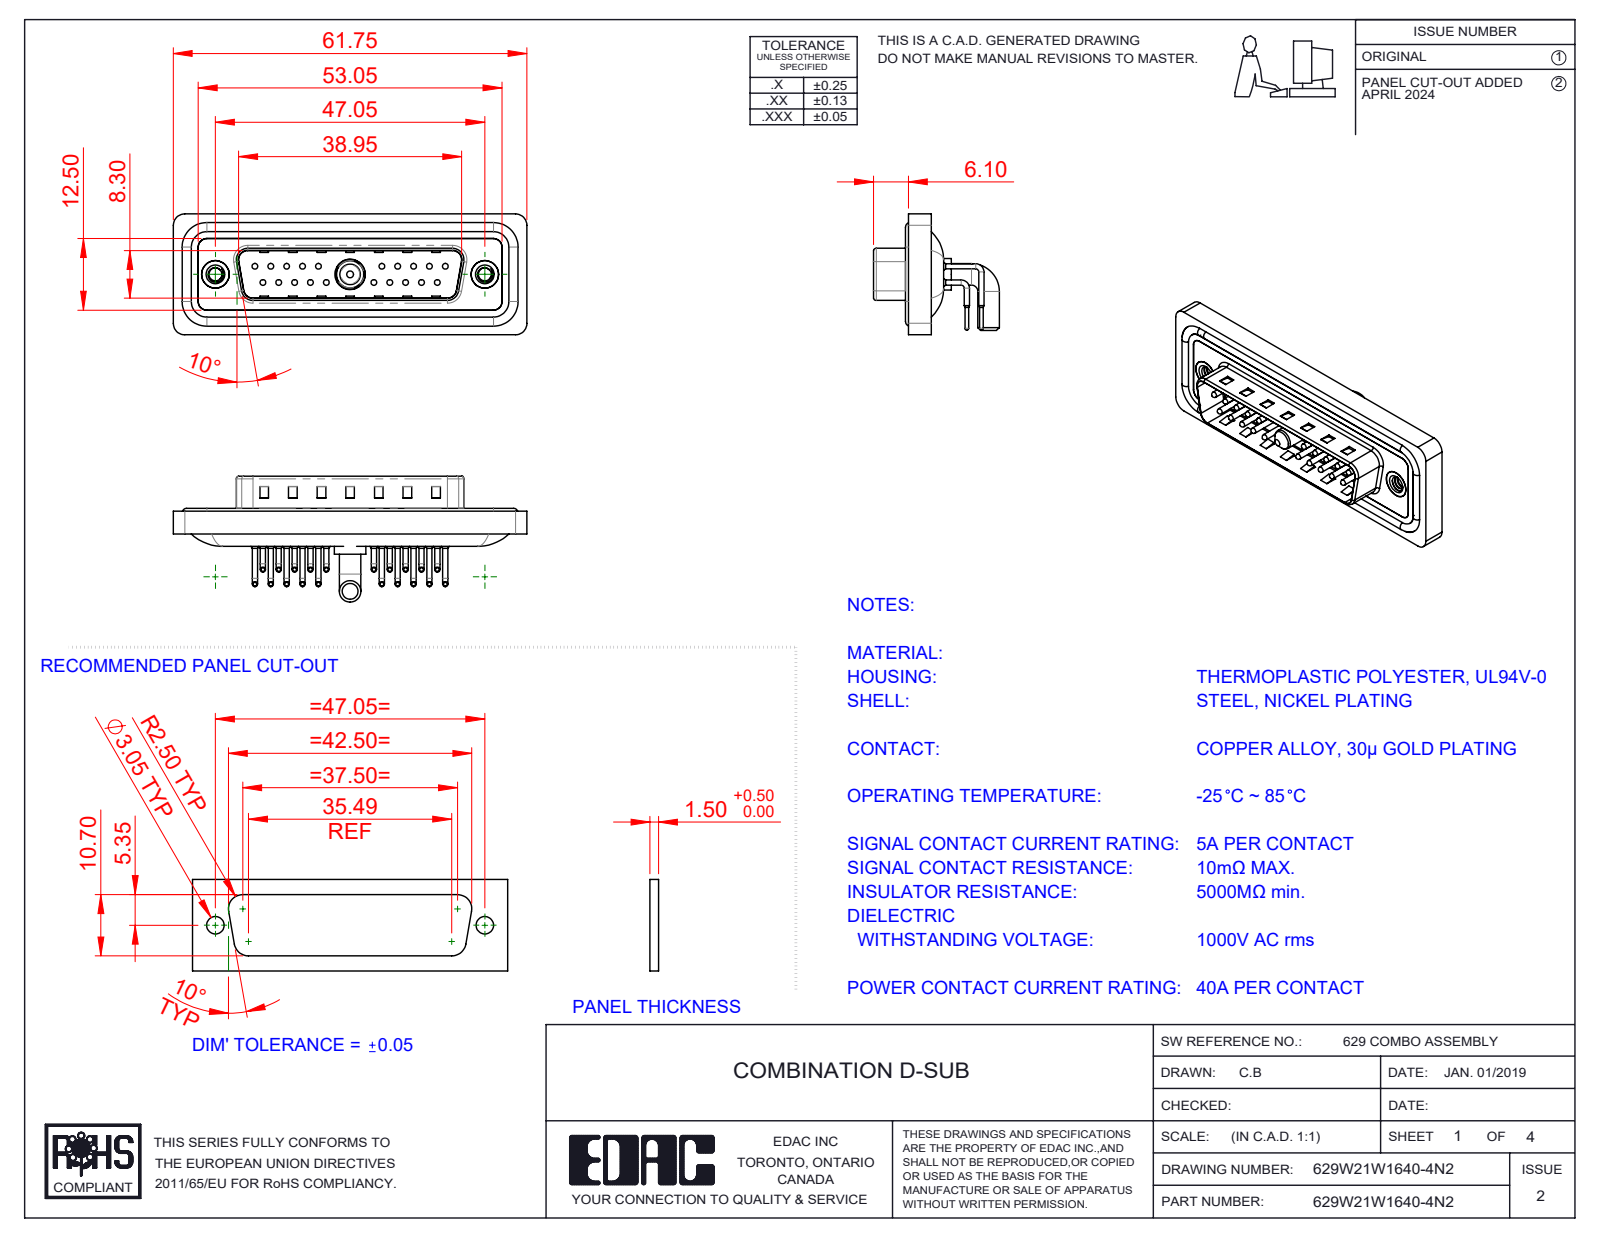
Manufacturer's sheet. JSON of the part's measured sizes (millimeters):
{"part_name": "629Combo Threaded Rivet_2; 629Combo Shell Front_25 Contacts; 629Combo Waterproof Housing_25 Contacts; 629Combo Shell Rear_25 Contacts (+5 more)", "step_written_by": "SolidWorks 2023 (CONFIG_CONTROL_DESIGN)", "units": "millimeters", "bodies": {"solids": 29, "faces": 2726, "planar": 1499, "cylindrical": 929, "other": 298}, "overall_size": [61.75, 21.98, 21.1], "volume_mm3": 7502, "surface_area_mm2": 12765, "round_holes": [[0.75, 20], [1.6, 20], [2, 20], [2.26, 2], [4, 2], [4.8, 2], [5, 2], [4.85, 1], [5.3, 1]], "round_bosses_or_shafts": [[0.9, 40], [1.5, 20], [1, 20], [0.65, 20], [1.6, 4], [4.9, 2], [3.75, 2], [5.5, 1]], "partial_cylinders_radius": [[1.01, 20], [1.5, 18], [2, 18], [0.5, 8], [1.6, 8], [0.25, 4], [0.6, 4], [0.65, 4]], "face_to_face_distances": [0.4, 2.9, 0.8, 4.1, 1.1, 2.1, 1.6, 4.5, 1.5, 2.5], "hole_center_spacings": [3.16, 2.77, 5.54, 8.31, 5.04, 19.39, 20.97, 22.16]}
